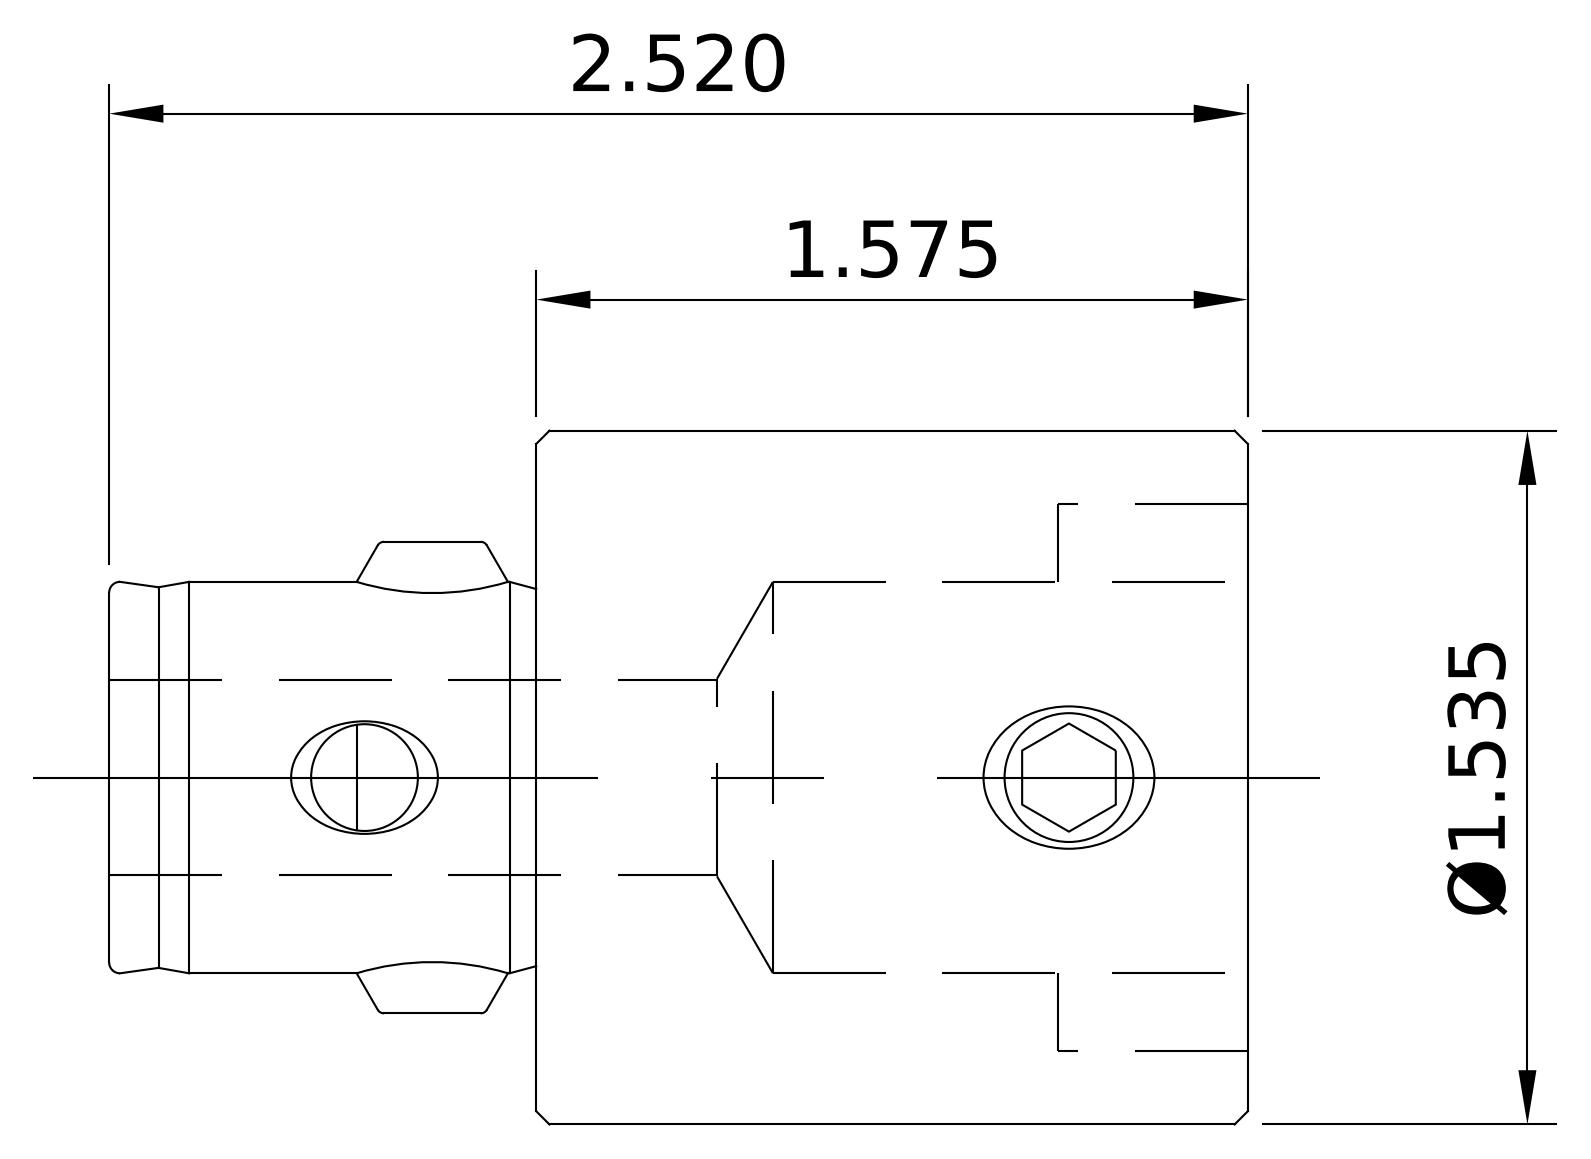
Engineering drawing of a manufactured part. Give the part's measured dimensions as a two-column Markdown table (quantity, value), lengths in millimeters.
| quantity | value |
| --- | --- |
| part name | 10.690.43X_10.690.434; 691-50XRing_10.691.504Ring; 10.691.50X_10.691.504; 11.331.440 (+1 more) |
| STEP written by | SolidWorks 2015 (AUTOMOTIVE_DESIGN) |
| units | millimeters |
| bodies | 4 solids, 136 faces (39 planar, 45 cylindrical, 52 other) |
| overall size | 84 × 39 × 39 |
| volume | 61 074 mm³ |
| surface area | 17 178 mm² |
| round holes (diameter × count) | 3.5 × 1, 6 × 1, 6.8 × 1, 8.2 × 1, 8.5 × 1, 10.5 × 1, 16.5 × 1, 22 × 1, 22.5 × 1 |
| round bosses / shafts (diameter × count) | 39 × 1, 38.6 × 1, 8.4 × 1, 8 × 1, 7 × 1, 5.5 × 1 |
| partial cylindrical surfaces (radius × count) | 3.5 × 2, 11 × 1 |
| main face-to-face distances | 60, 24, 84, 55, 31, 29, 18.9, 73.4, 49.4, 18.4 |
| hole center spacings | 15.25, 59.6 |
